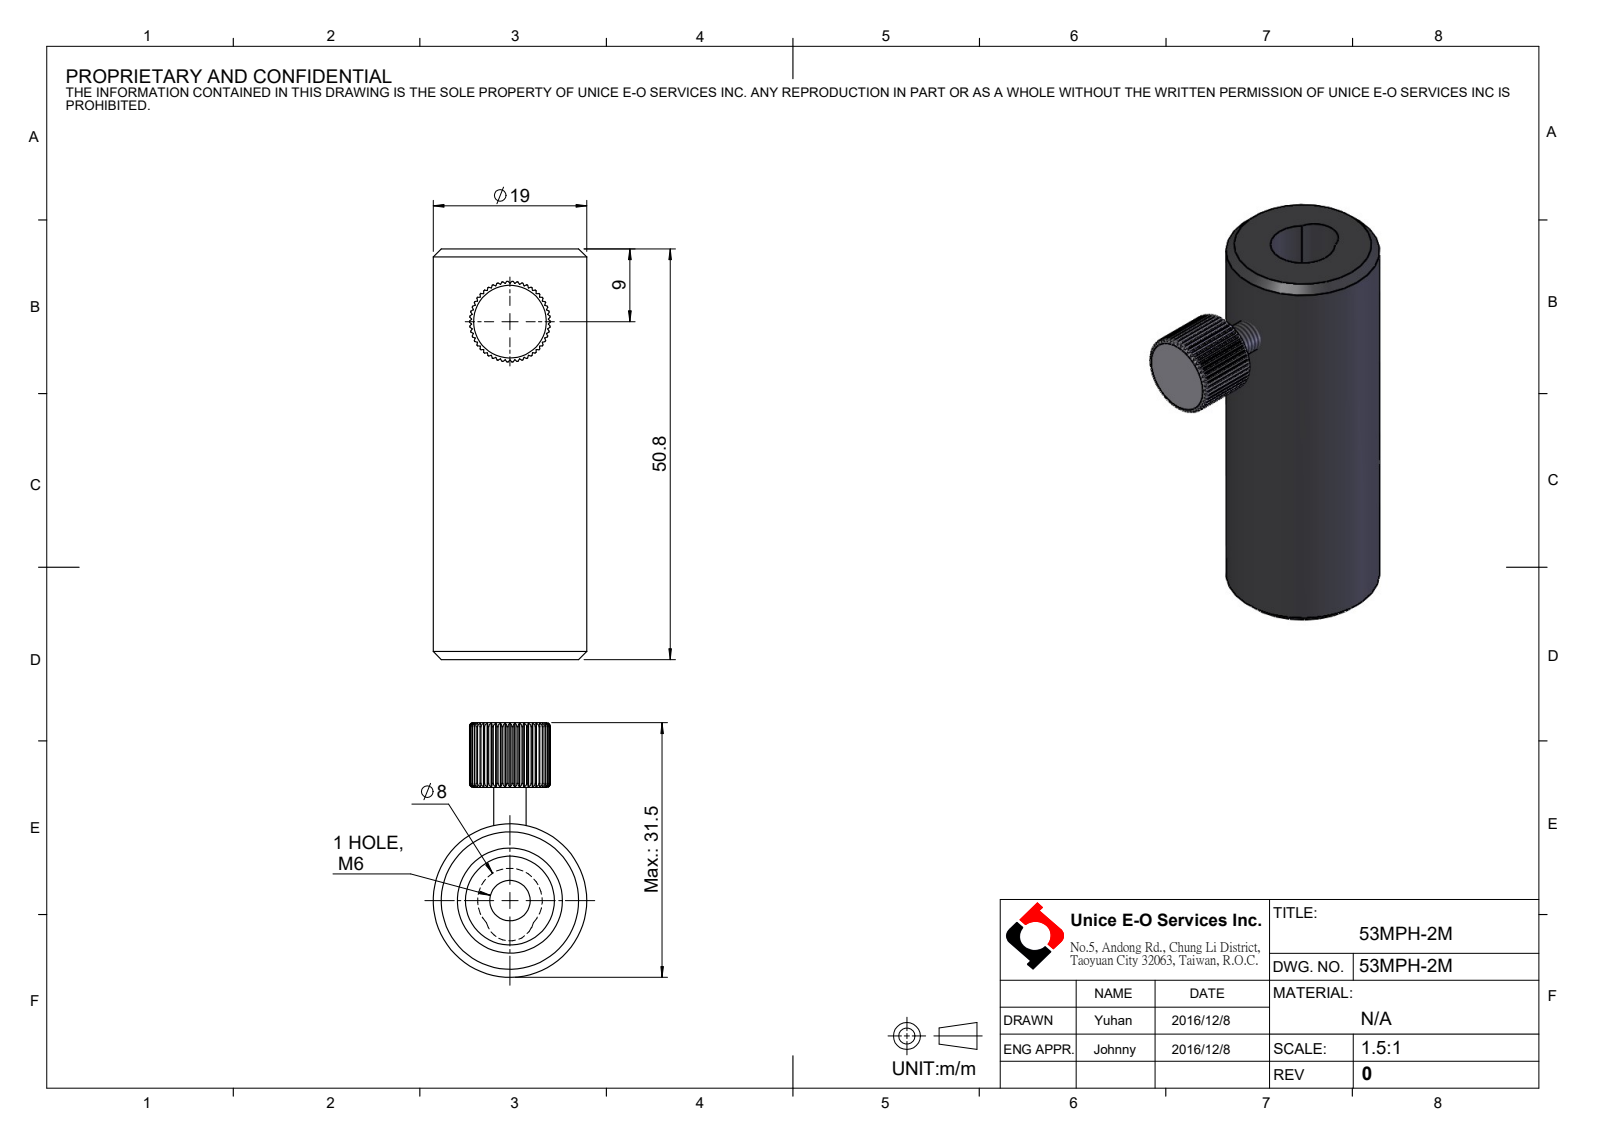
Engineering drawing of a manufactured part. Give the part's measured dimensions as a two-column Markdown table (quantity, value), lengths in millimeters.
| quantity | value |
| --- | --- |
| part name | 53MPH-2M |
| STEP written by | SolidWorks 2016 (CONFIG_CONTROL_DESIGN) |
| units | millimeters |
| bodies | 3 solids, 251 faces (108 planar, 129 cylindrical, 14 other) |
| overall size | 50.8 × 31.5 × 19 |
| volume | 12 407 mm³ |
| surface area | 5 995 mm² |
| round holes (diameter × count) | 3.3 × 1, 5 × 1, 13 × 1 |
| round bosses / shafts (diameter × count) | 19 × 1, 4 × 1 |
| partial cylindrical surfaces (radius × count) | 3 × 1, 4 × 1, 5 × 1 |
| main face-to-face distances | 50.8, 6, 44.8, 6.72, 8, 6.71, 10, 18 |
